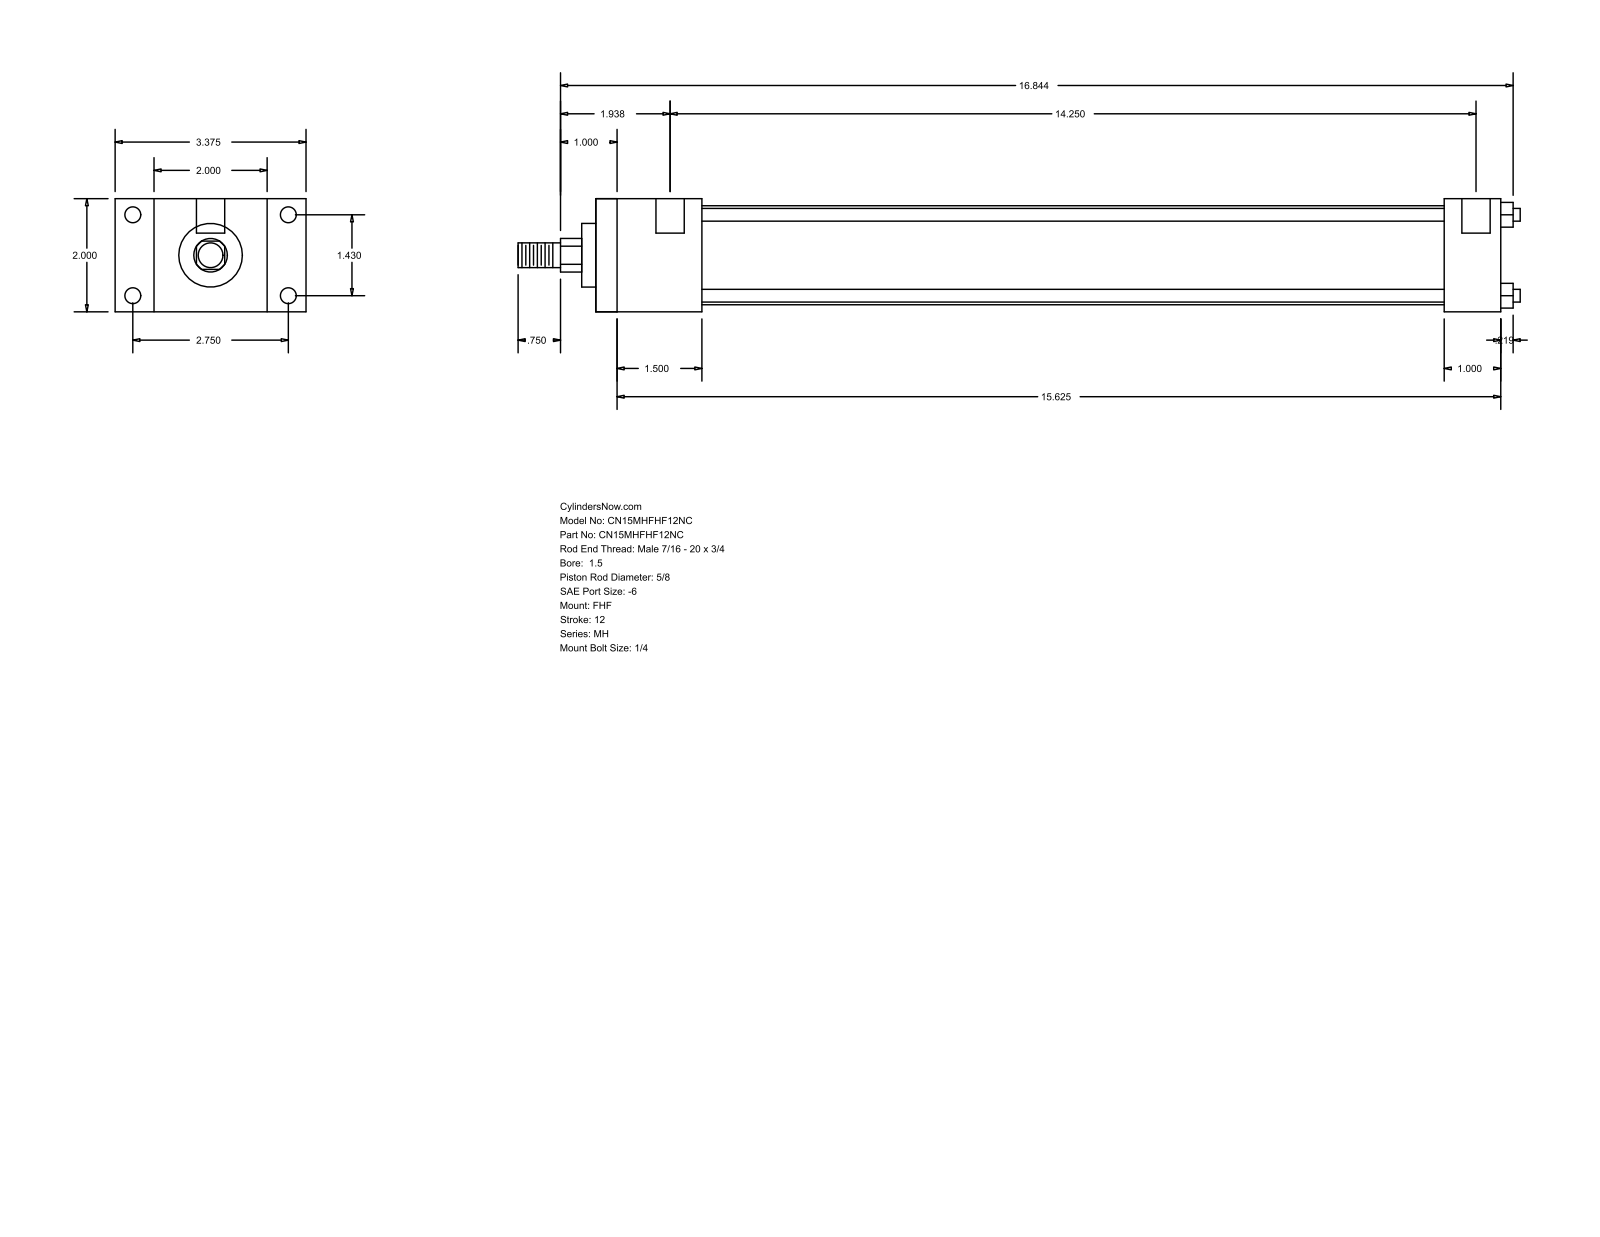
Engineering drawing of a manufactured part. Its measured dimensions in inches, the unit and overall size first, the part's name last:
Units: inches
Overall size (bounding box): 17.719 × 3.375 × 2
Round holes (diameter × count): ⌀0.219 ×4, ⌀0.281 ×4, ⌀0.5 ×2
Round bosses / shafts (diameter × count): ⌀0.225 ×4, ⌀1.75 ×1, ⌀1.125 ×1, ⌀0.625 ×1, ⌀0.437 ×1
Partial cylindrical surfaces — rounded edges, fillets, slot ends (radius × count): R0.297 ×1
Main face-to-face distances: 2, 0.687, 2.687, 1.875, 3.375, 16, 14.125, 15, 13.125, 1
Hole centre spacings: 1.43, 2.75, 3.099, 14.375, 0.125, 14.25
Bodies: 0 solids, 88 faces (60 planar, 28 cylindrical, 0 other)
Part name (STEP PRODUCT): MH_FHF__0150_0.625
STEP written by: GSSL Pune (CONFIG_CONTROL_DESIGN)
